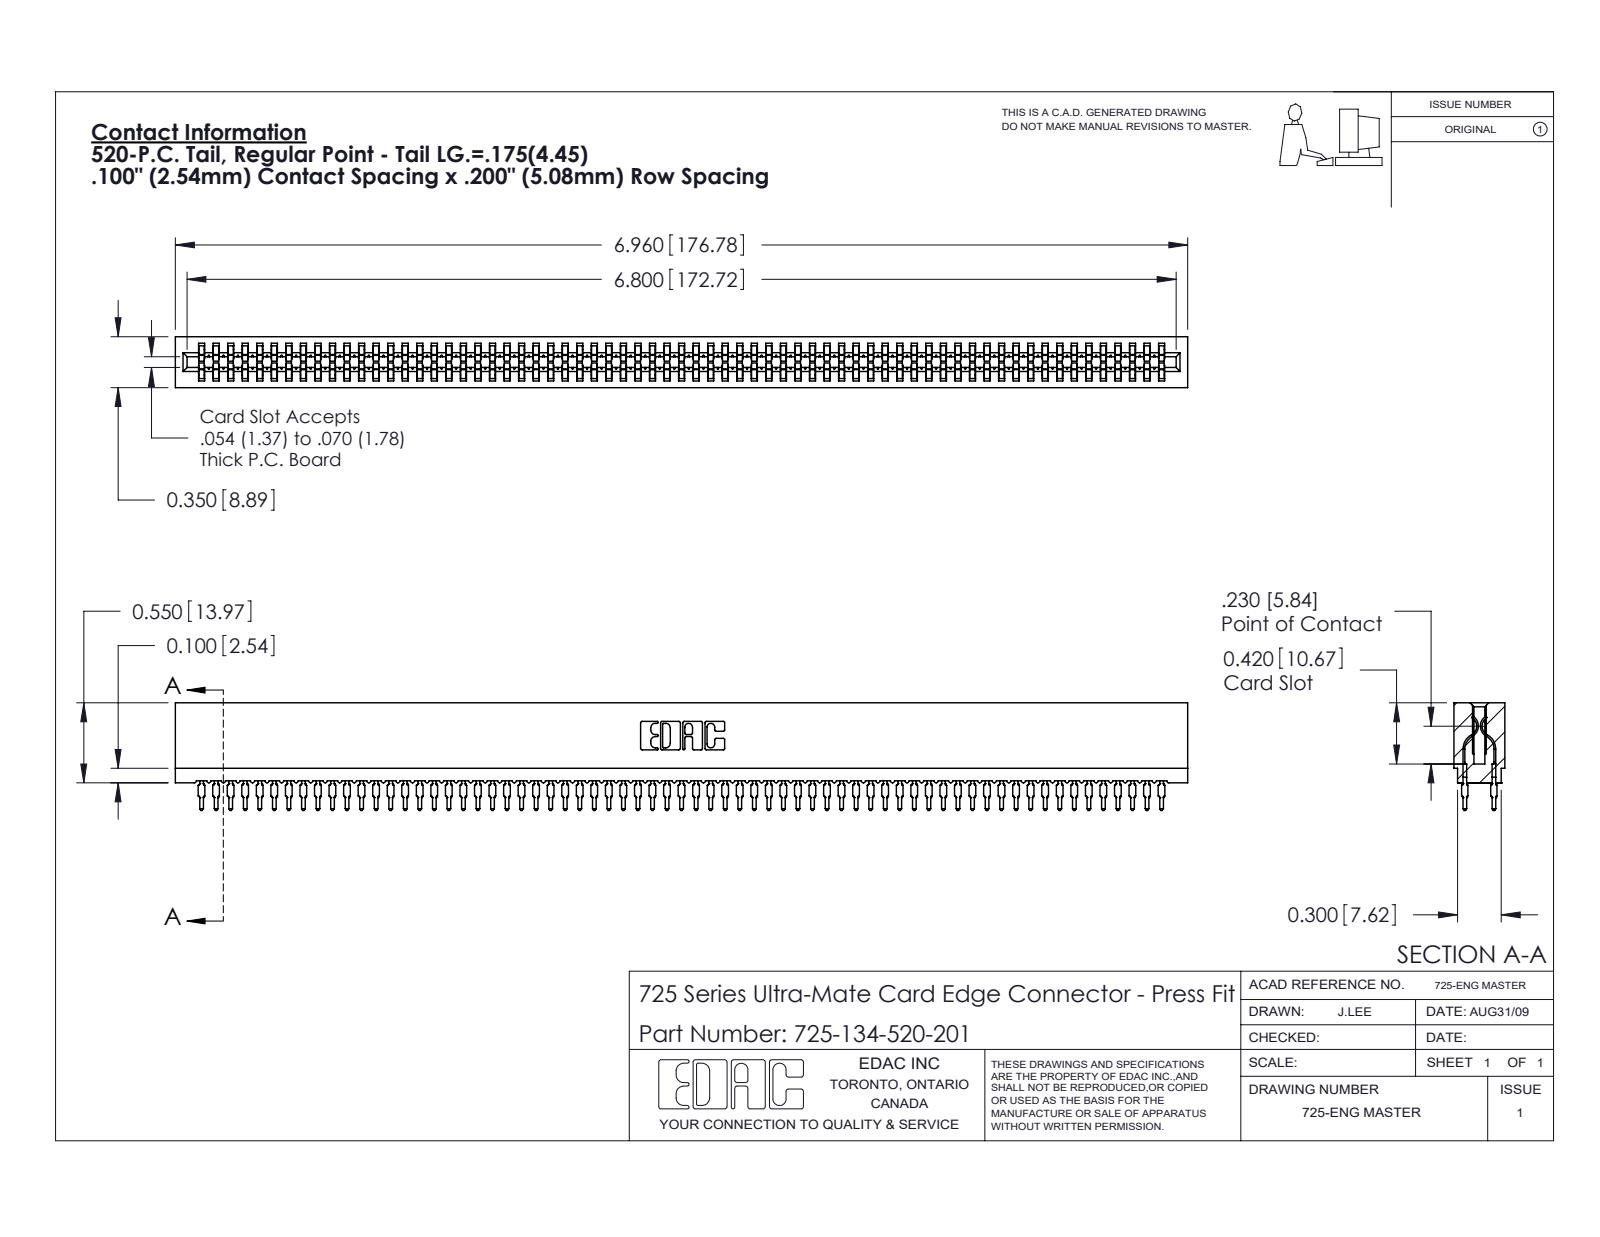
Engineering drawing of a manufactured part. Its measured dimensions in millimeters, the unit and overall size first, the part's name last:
Units: millimetres
Overall size (bounding box): 176.8 × 18.8 × 8.9
Partial cylindrical surfaces — rounded edges, fillets, slot ends (radius × count): R0.5 ×268, R0.4 ×134, R0.3 ×22, R0.1 ×8, R0.3 ×8, R0.2 ×6, R0.8 ×6, R0.7 ×3
Main face-to-face distances: 8.9, 1.6, 7.3, 5.4, 3.5, 1.9, 3.8, 1.1, 7.7, 0.5
Volume: 13 800 mm³ · Surface area: 29 070 mm²
Bodies: 135 solids, 12088 faces (6219 planar, 2385 cylindrical, 3484 other)
Part name (STEP PRODUCT): 725-134-520-201; 745-292-001_520; 725 Part_Insulator Option - 01
STEP written by: SolidWorks 2020 (CONFIG_CONTROL_DESIGN)
